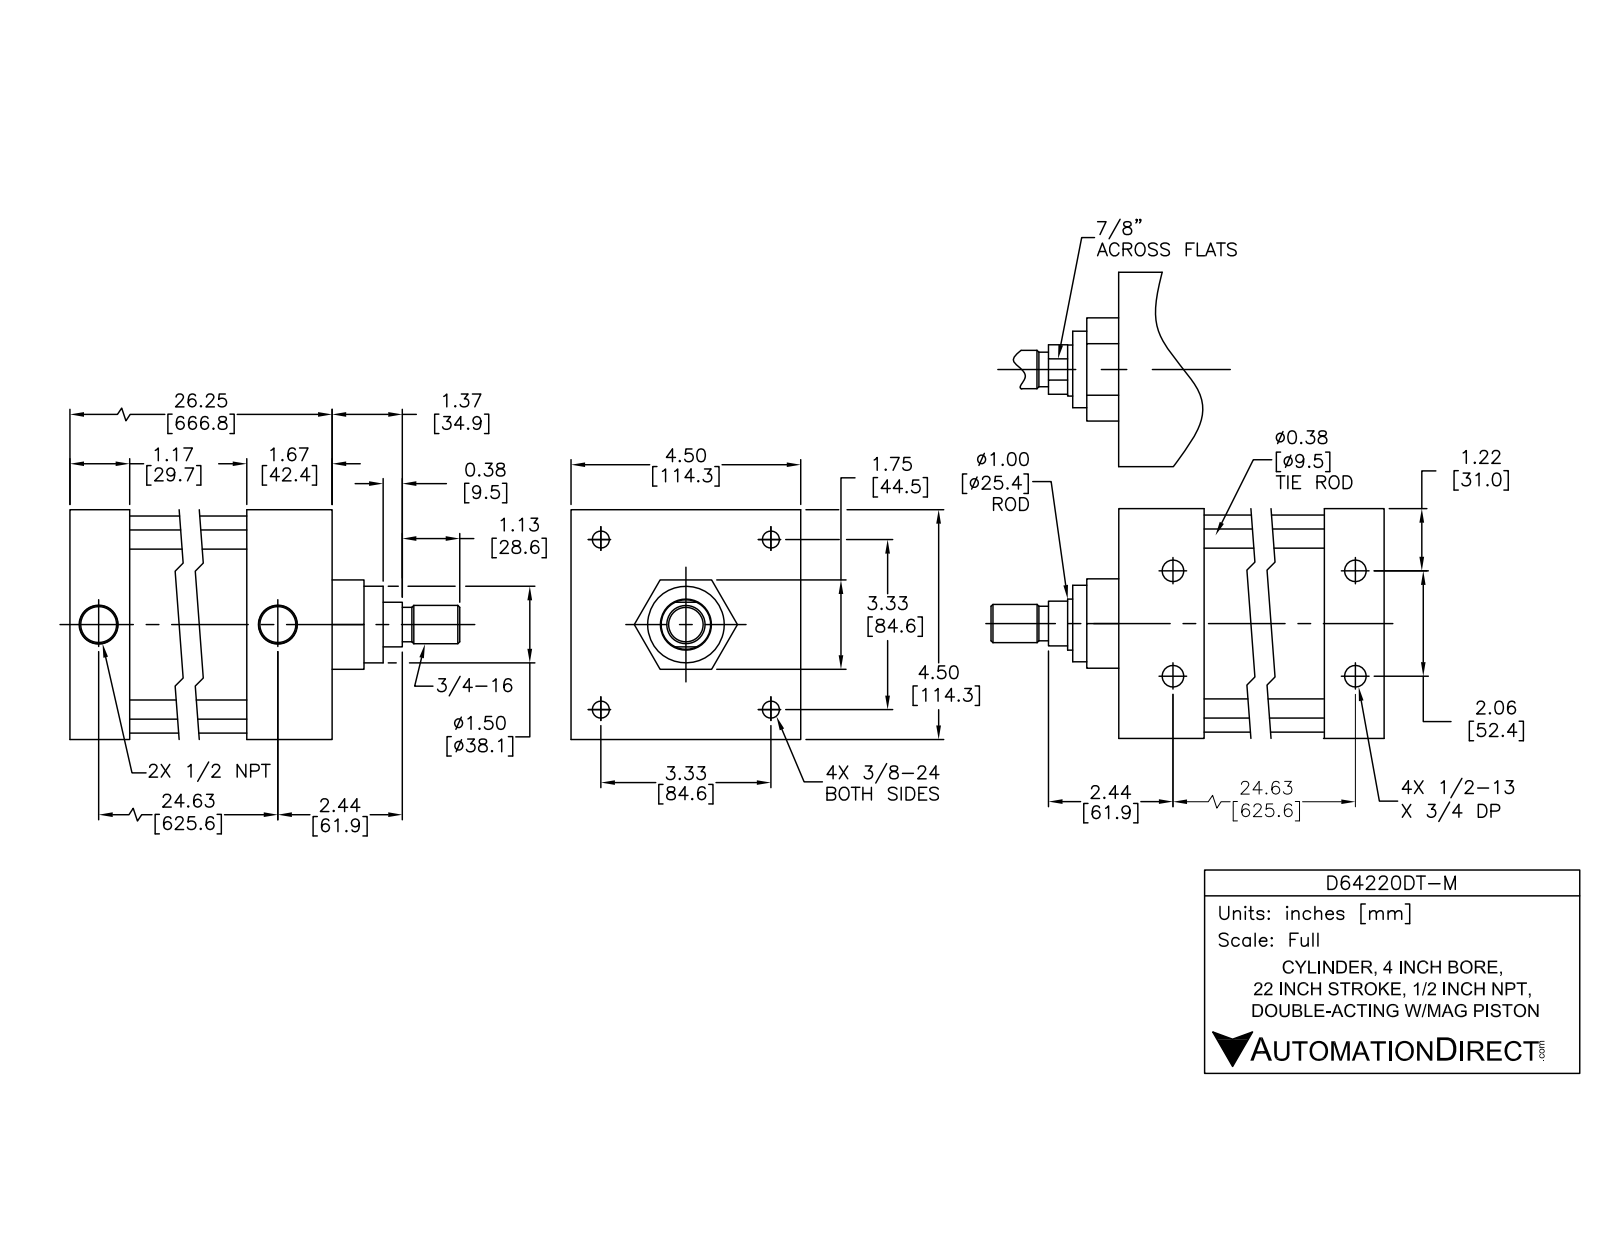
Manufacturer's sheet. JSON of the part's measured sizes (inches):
{"part_name": "D64220DT-M BODY; D64220DT-M PISTON; D64220DT-M", "step_written_by": "SolidWorks 2015 (AUTOMOTIVE_DESIGN)", "units": "inches", "bodies": {"solids": 12, "faces": 303, "planar": 99, "cylindrical": 114, "other": 90}, "overall_size": [28.745, 4.5, 4.5], "volume_in3": 138.1, "surface_area_in2": 1023, "round_holes": [[0.33, 4], [0.406, 4], [0.417, 4], [0.625, 4], [0.5, 2], [0.766, 2], [1, 1], [1.003, 1], [4, 1]], "round_bosses_or_shafts": [[0.609, 4], [0.375, 4], [0.34, 4], [4.25, 1], [3.997, 1], [1.75, 1], [0.997, 1], [0.97, 1]], "partial_cylinders_radius": [[0.45, 4]], "face_to_face_distances": [4.5, 0.08, 23.326, 26.246, 1.75, 24.997, 1.249, 23.751, 1.246, 2.495], "hole_center_spacings": [2.349, 3.322, 24.644, 24.622, 1.031, 1.031, 2.062, 4.698]}
